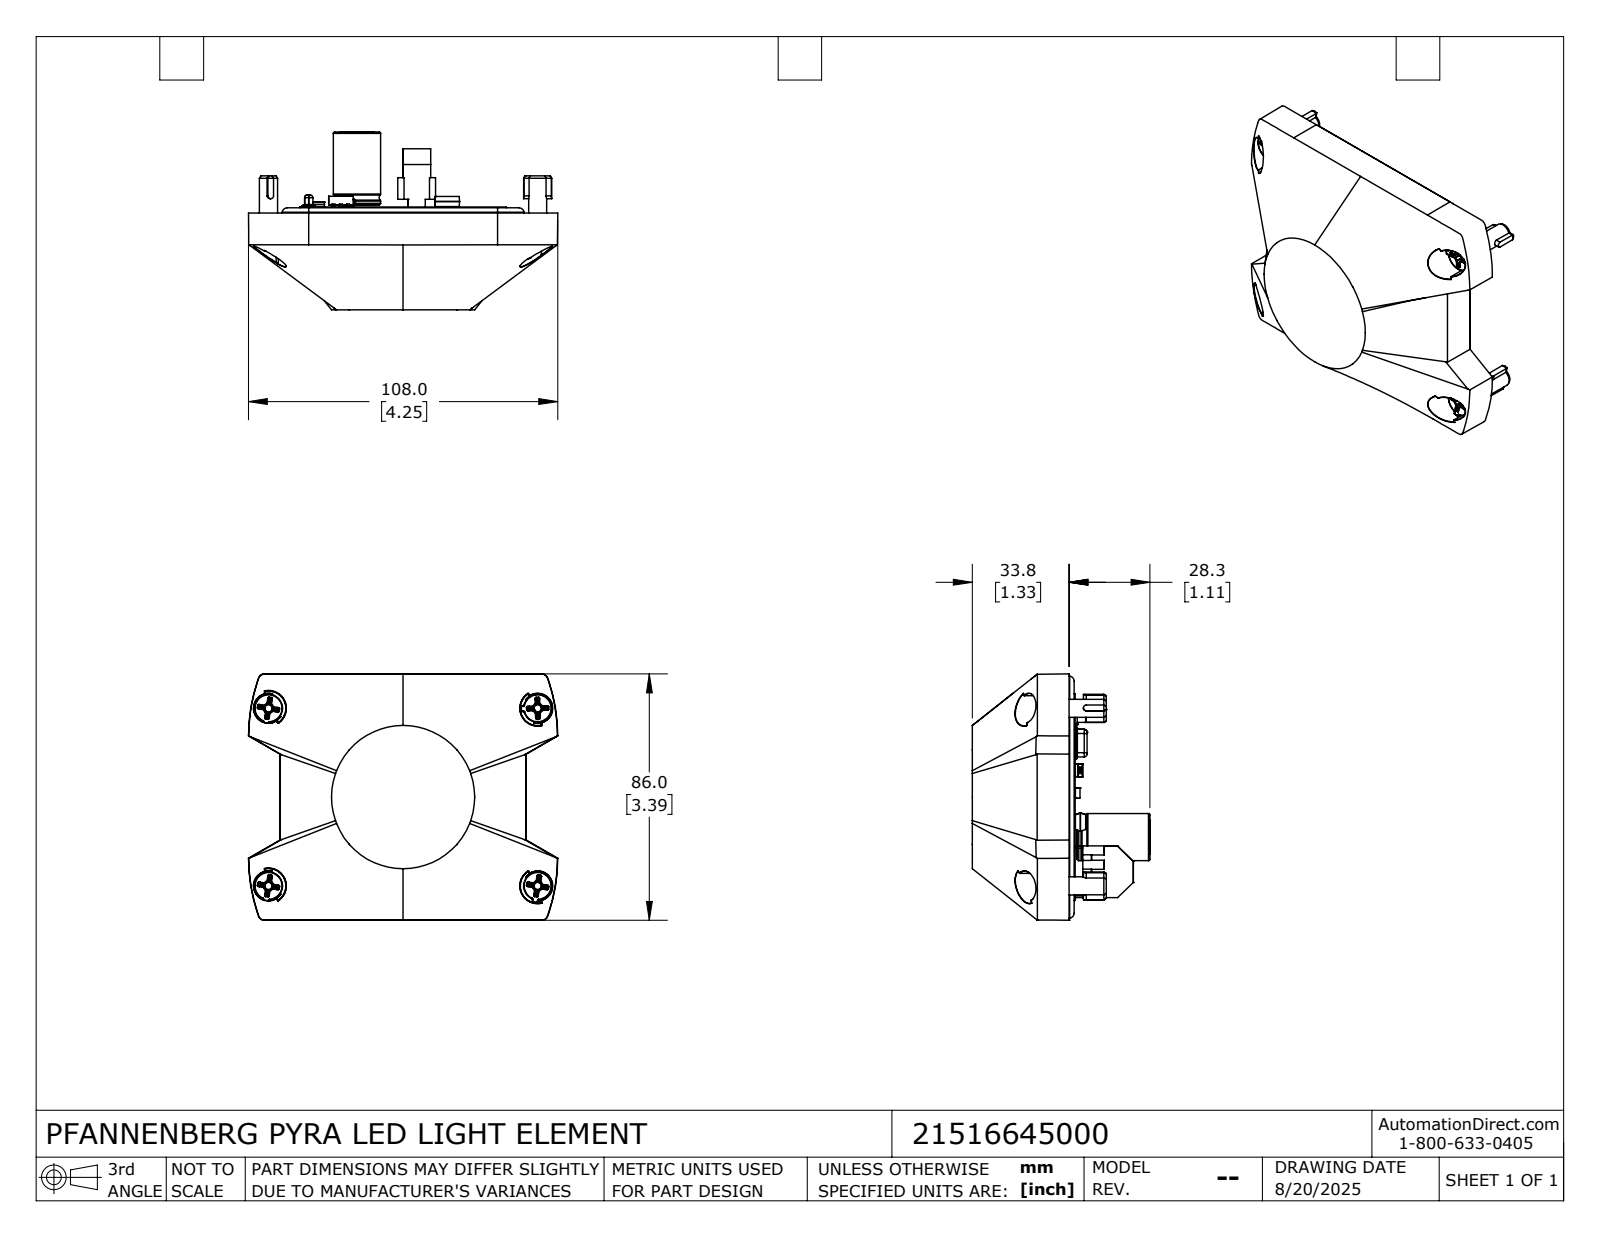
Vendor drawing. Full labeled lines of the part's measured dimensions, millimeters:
Part name (STEP PRODUCT): 21516645000
STEP written by: SolidWorks 2024 (CONFIG_CONTROL_DESIGN)
Units: millimetres
Bodies: 17 solids, 1949 faces (787 planar, 409 cylindrical, 753 other)
Overall size (bounding box): 108 × 86 × 62.07
Volume: 219 200 mm³ · Surface area: 53 231 mm²
Round holes (diameter × count): ⌀1 ×12, ⌀0.8 ×8, ⌀1.1 ×7, ⌀0.9 ×2, ⌀1.4 ×2, ⌀1.5 ×2, ⌀2.5 ×2, ⌀3 ×2, ⌀1.02 ×1, ⌀2.46 ×1, ⌀3.47 ×1, ⌀4.11 ×1
Round bosses / shafts (diameter × count): ⌀9.8 ×4, ⌀6.3 ×4, ⌀16.5 ×1
Partial cylindrical surfaces — rounded edges, fillets, slot ends (radius × count): R0.2 ×111, R0.1 ×8, R1 ×8, R1.6 ×8, R0.5 ×5, R1.44 ×4, R1.74 ×4, R1.84 ×4
Main face-to-face distances: 1.62, 3.5, 5.12, 35.92, 34.3, 30.8, 81.77, 81, 0.77, 0.5
Hole centre spacings: 5.08, 15, 37.94, 47.77, 4.77, 5, 10, 10.16
